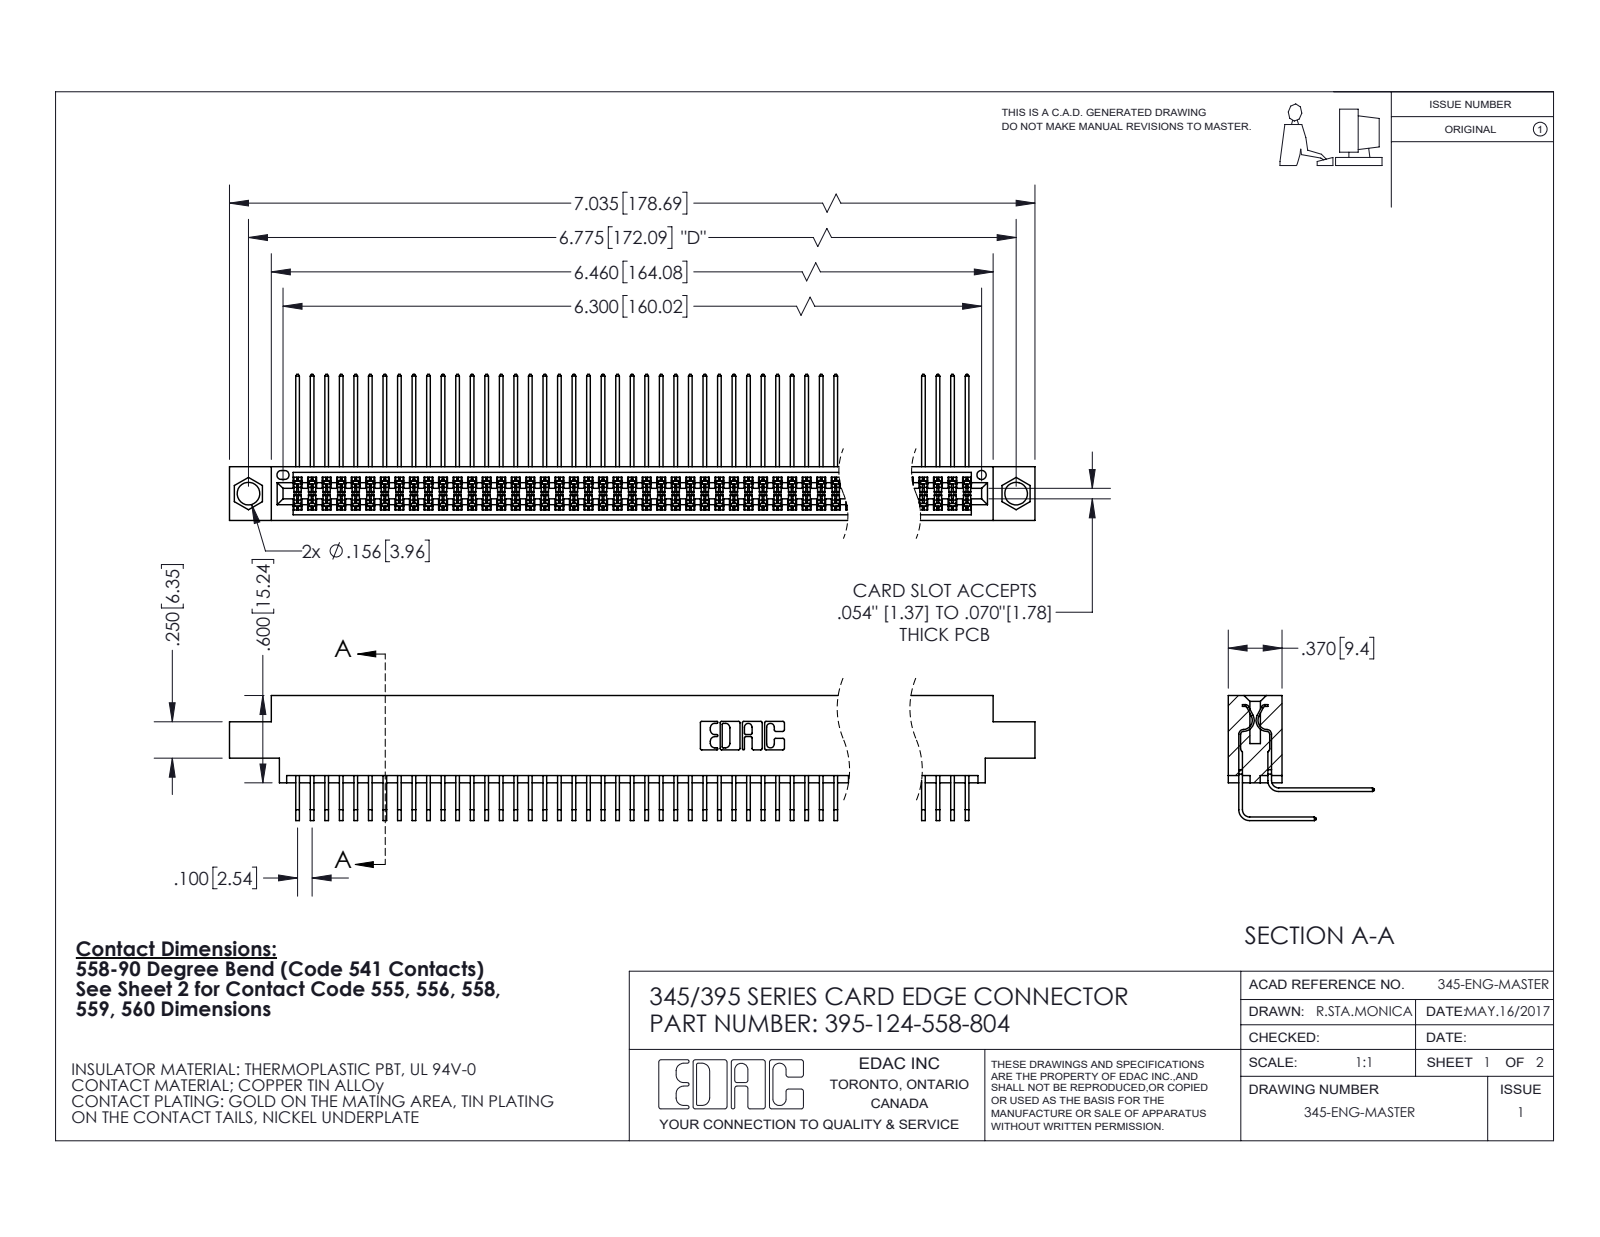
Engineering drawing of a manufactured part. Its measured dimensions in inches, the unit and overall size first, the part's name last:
Units: inches
Overall size (bounding box): 7.035 × 1.005 × 0.859
Round holes (diameter × count): ⌀0.156 ×2, ⌀0.064 ×1
Partial cylindrical surfaces — rounded edges, fillets, slot ends (radius × count): R0.006 ×186, R0.01 ×22, R0.007 ×6, R0.031 ×6, R0.026 ×3, R0.014 ×2, R0.019 ×2, R0.022 ×2
Main face-to-face distances: 0.072, 0.298, 0.2, 0.37, 0.098, 0.272, 0.025, 0.225, 0.175, 0.025
Hole centre spacings: 0.27, 6.539, 6.775
Volume: 1.101 in³ · Surface area: 47.14 in²
Bodies: 125 solids, 6592 faces (4438 planar, 2154 cylindrical, 0 other)
Part name (STEP PRODUCT): 345 Part_0.170 Offset - 0.156 Dia-TI; 395-124-558-804; 345-292-001_558 Tail - 2; 345-292-001_558 559 Tail - 1
STEP written by: SolidWorks 2020 (CONFIG_CONTROL_DESIGN)
